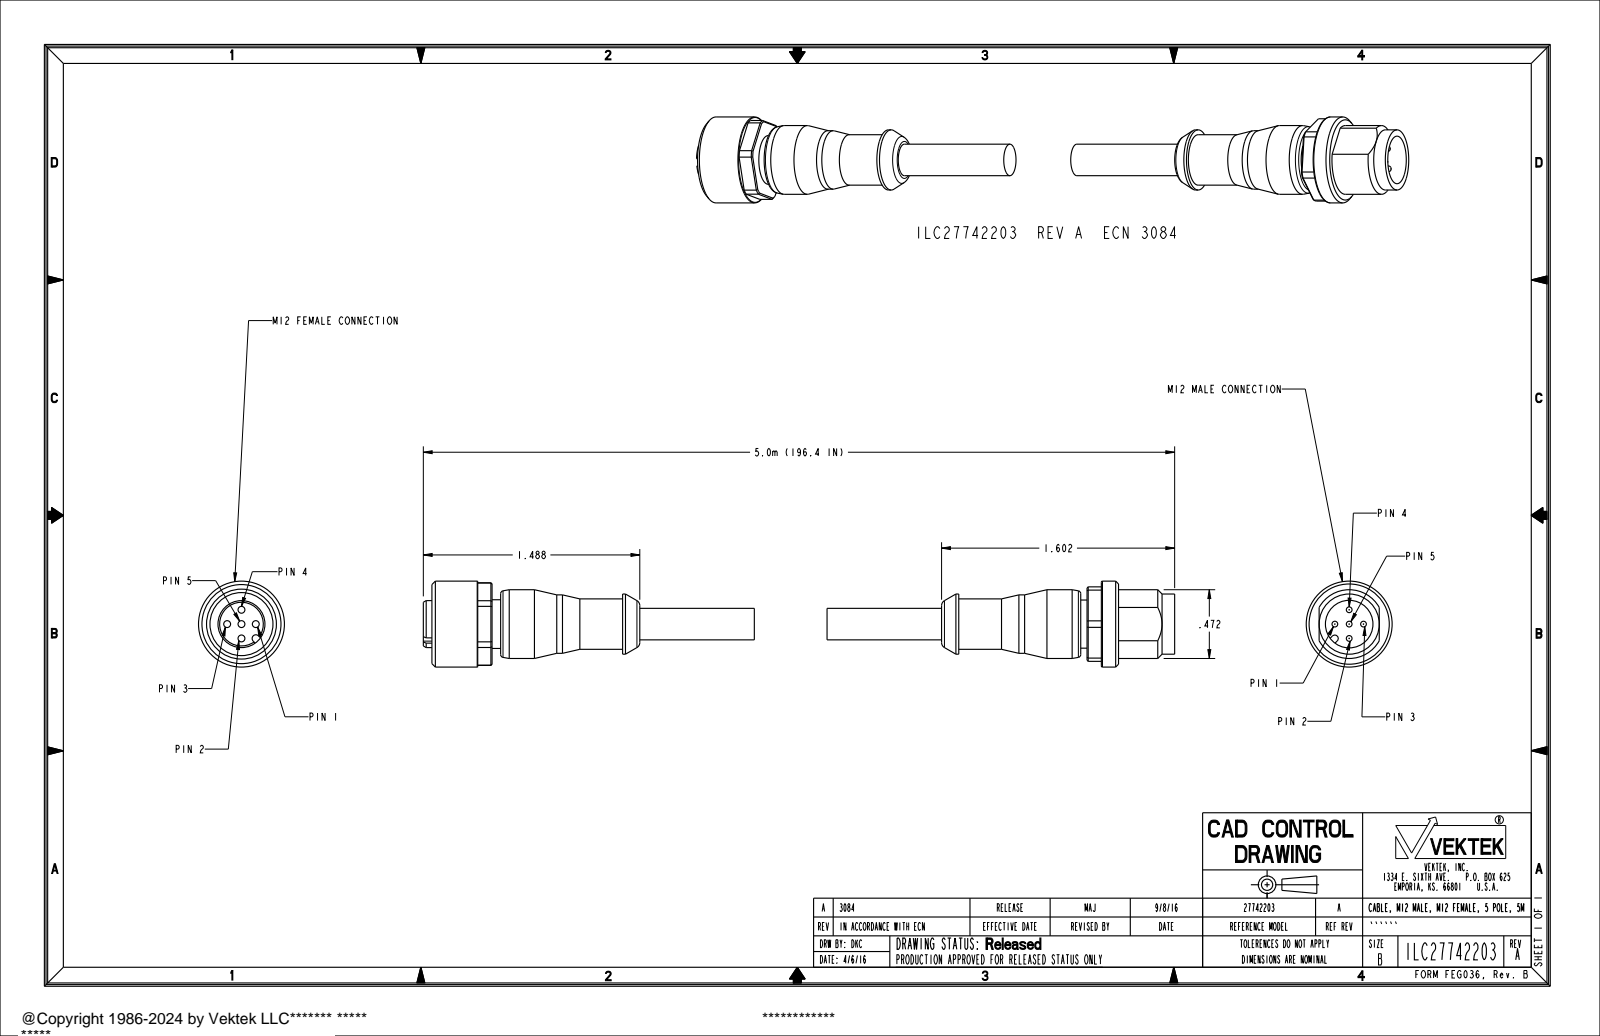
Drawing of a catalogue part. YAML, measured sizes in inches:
part_name: "27742203_1; 27742203_2; ILC27742203"
step_written_by: "PRO/ENGINEER BY PARAMETRIC TECHNOLOGY CORPORATION, 2013320 (AUTOMOTIVE_DESIGN)"
units: inches
bodies: {solids: 2, faces: 203, planar: 60, cylindrical: 72, other: 71}
overall_size: [5.165, 0.591, 0.591]
volume: 0.488
surface_area: 8.004
round_holes:
  - {diameter: 0.047, count: 5}
  - {diameter: 0.327, count: 1}
  - {diameter: 0.433, count: 1}
round_bosses_or_shafts:
  - {diameter: 0.039, count: 5}
  - {diameter: 0.591, count: 1}
  - {diameter: 0.472, count: 1}
  - {diameter: 0.413, count: 1}
  - {diameter: 0.402, count: 1}
  - {diameter: 0.346, count: 1}
  - {diameter: 0.335, count: 1}
  - {diameter: 0.331, count: 1}
partial_cylinders:
  - {radius: 0.024, count: 1}
  - {radius: 0.026, count: 1}
  - {radius: 0.283, count: 1}
face_to_face_distances: [0.512, 0.118, 4.091, 0.413, 4.461, 0.472, 4.307, 0.295, 0.059, 0.098]
hole_center_spacings: [0.098, 0.139, 0.197]
